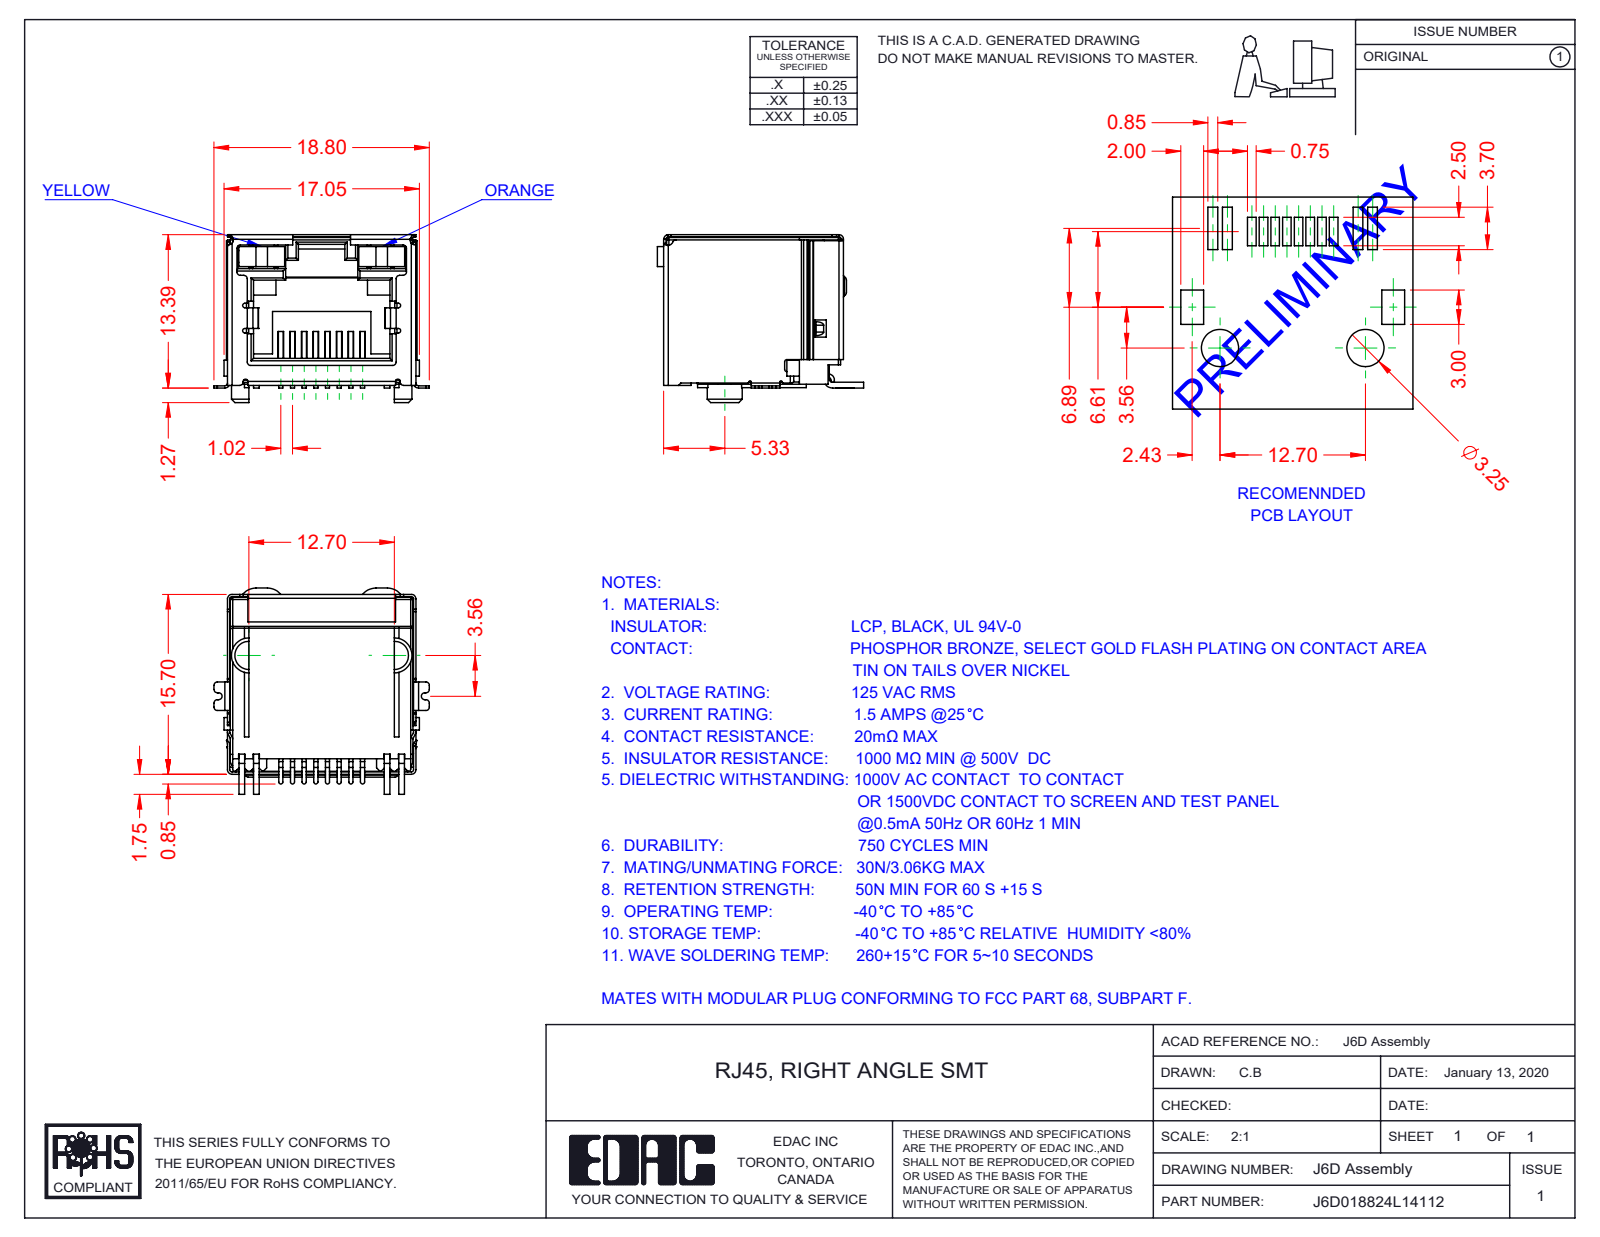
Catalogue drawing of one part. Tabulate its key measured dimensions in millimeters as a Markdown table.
| quantity | value |
| --- | --- |
| part name | 6D Insulator; 6D LED LH_1-Yellow; 6D LED RH_4-Orange; 6D Shield_LED - No EMI (+2 more) |
| STEP written by | SolidWorks 2016 (CONFIG_CONTROL_DESIGN) |
| units | millimeters |
| bodies | 12 solids, 893 faces (644 planar, 216 cylindrical, 33 other) |
| overall size | 18.8 × 18 × 14.65 |
| volume | 1 804 mm³ |
| surface area | 4 898 mm² |
| partial cylindrical surfaces (radius × count) | 0.3 × 39, 0.2 × 37, 0.4 × 16, 0.1 × 12, 0.15 × 8, 0.18 × 8, 0.5 × 6, 1.5 × 5 |
| main face-to-face distances | 16, 16.25, 16.2, 2.25, 1, 15.95, 16.05, 12.8, 0.45, 16.45 |
